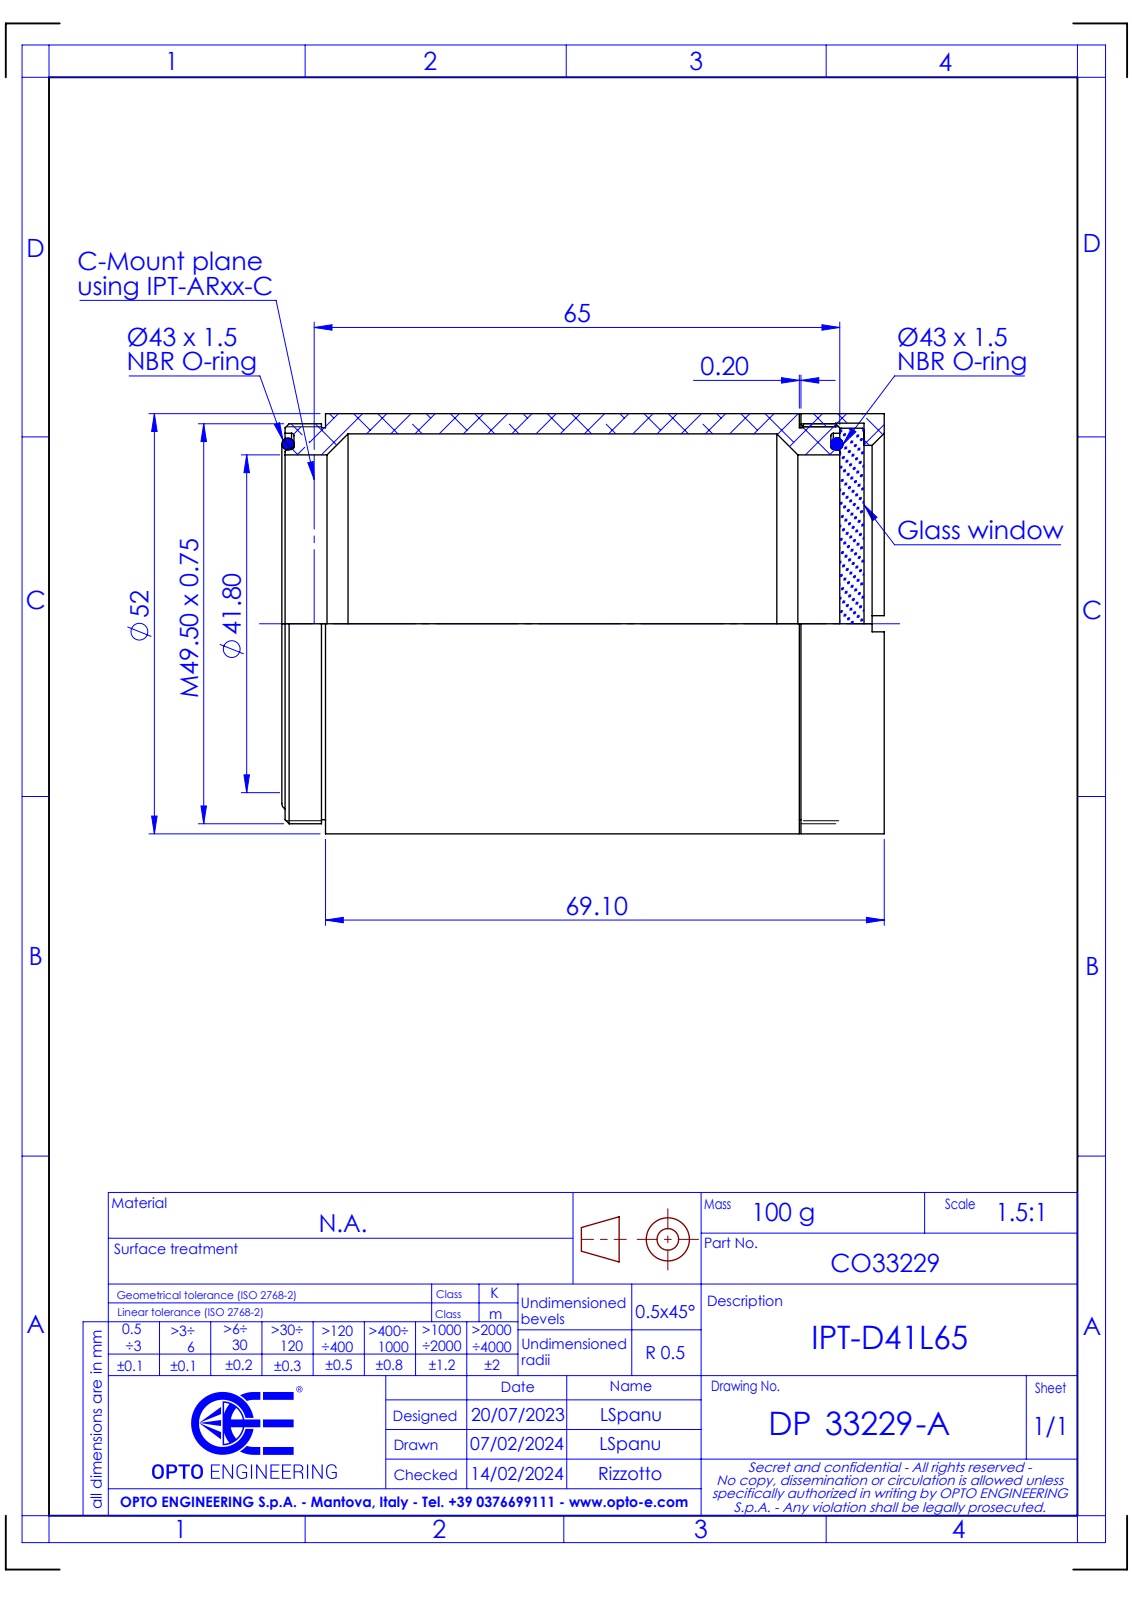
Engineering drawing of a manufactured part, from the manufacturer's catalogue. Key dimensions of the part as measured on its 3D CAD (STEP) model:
Part name (STEP PRODUCT): DP33229-A_IPT-D41L65
STEP written by: SolidWorks 2021 (CONFIG_CONTROL_DESIGN)
Units: millimetres
Bodies: 0 solids, 45 faces (15 planar, 16 cylindrical, 14 other)
Overall size (bounding box): 74.5 × 52 × 52
Round holes (diameter × count): ⌀41.8 ×1, ⌀44.15 ×1, ⌀47 ×1, ⌀47.15 ×1
Round bosses / shafts (diameter × count): ⌀52 ×1, ⌀49.5 ×1, ⌀48.5 ×1
Main face-to-face distances: 2.5, 66.6, 69.1, 58.6, 8, 10.5, 58.8, 7.8, 10.3, 3.9
